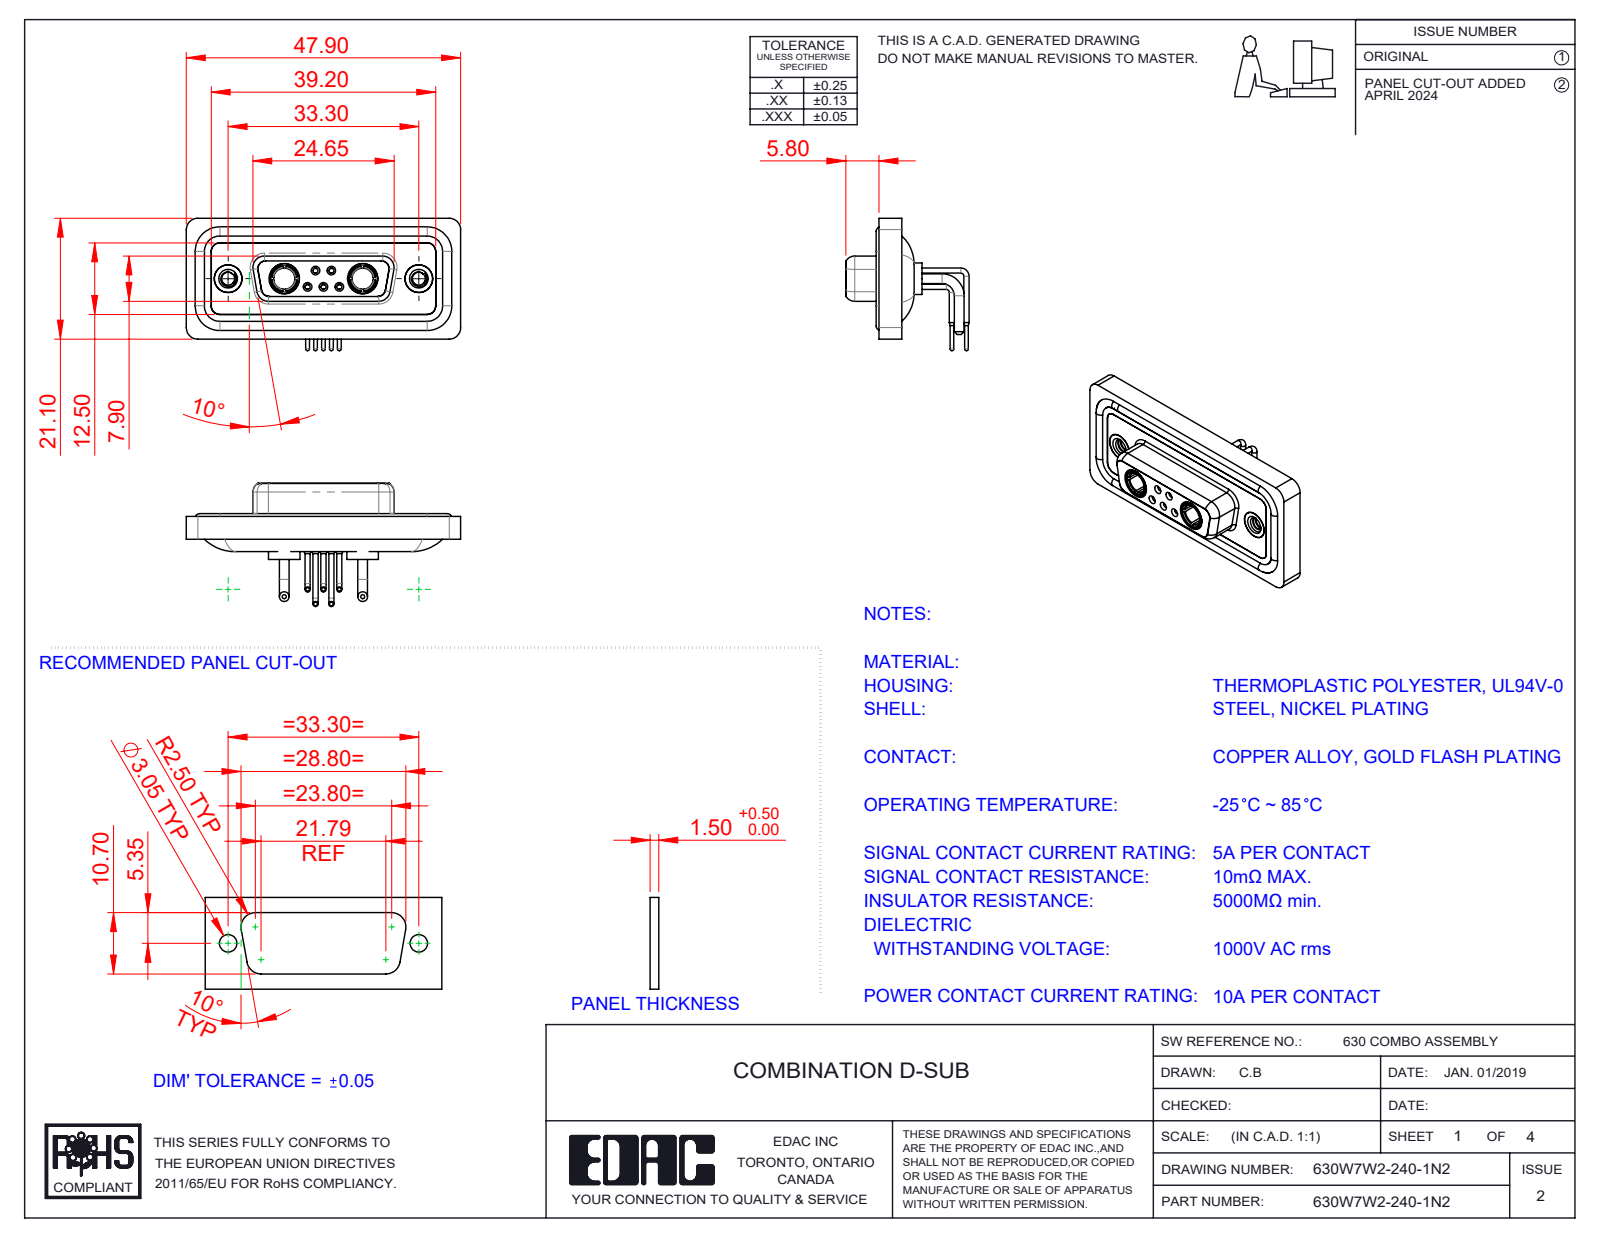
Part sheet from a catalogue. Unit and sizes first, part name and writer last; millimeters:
Units: millimetres
Overall size (bounding box): 47.9 × 23.12 × 21.53
Round holes (diameter × count): ⌀0.9 ×5, ⌀1.1 ×5, ⌀1.5 ×5, ⌀2 ×5, ⌀4.85 ×4, ⌀1.6 ×3, ⌀1.7 ×2, ⌀2.26 ×2, ⌀3.7 ×2, ⌀4 ×2, ⌀4.05 ×2, ⌀5 ×2
Round bosses / shafts (diameter × count): ⌀1.6 ×6, ⌀0.9 ×5, ⌀0.65 ×5, ⌀1.7 ×4, ⌀5.5 ×2, ⌀5.2 ×2, ⌀4.96 ×2, ⌀4.95 ×2
Partial cylindrical surfaces — rounded edges, fillets, slot ends (radius × count): R2 ×20, R1.5 ×18, R1.35 ×12, R1.6 ×8, R0.25 ×4, R0.5 ×4, R0.6 ×4, R0.65 ×4
Main face-to-face distances: 0.4, 1.8, 1.1, 1.6, 2.5, 2.9, 3.1, 3.7, 4.1, 1.5
Hole centre spacings: 3.16, 2.77, 9.8, 23.5, 4.31, 4.33, 5.03, 5.04
Volume: 6 081 mm³ · Surface area: 10 104 mm²
Bodies: 16 solids, 807 faces (238 planar, 353 cylindrical, 216 other)
Part name (STEP PRODUCT): 630Combo Contact Row 2_50 Contacts; 630W7W2-140-1N2; 630Combo Shell Rear_15 Contacts; 630Combo Waterproof Housing_15 Contacts (+5 more)
STEP written by: SolidWorks 2023 (CONFIG_CONTROL_DESIGN)
